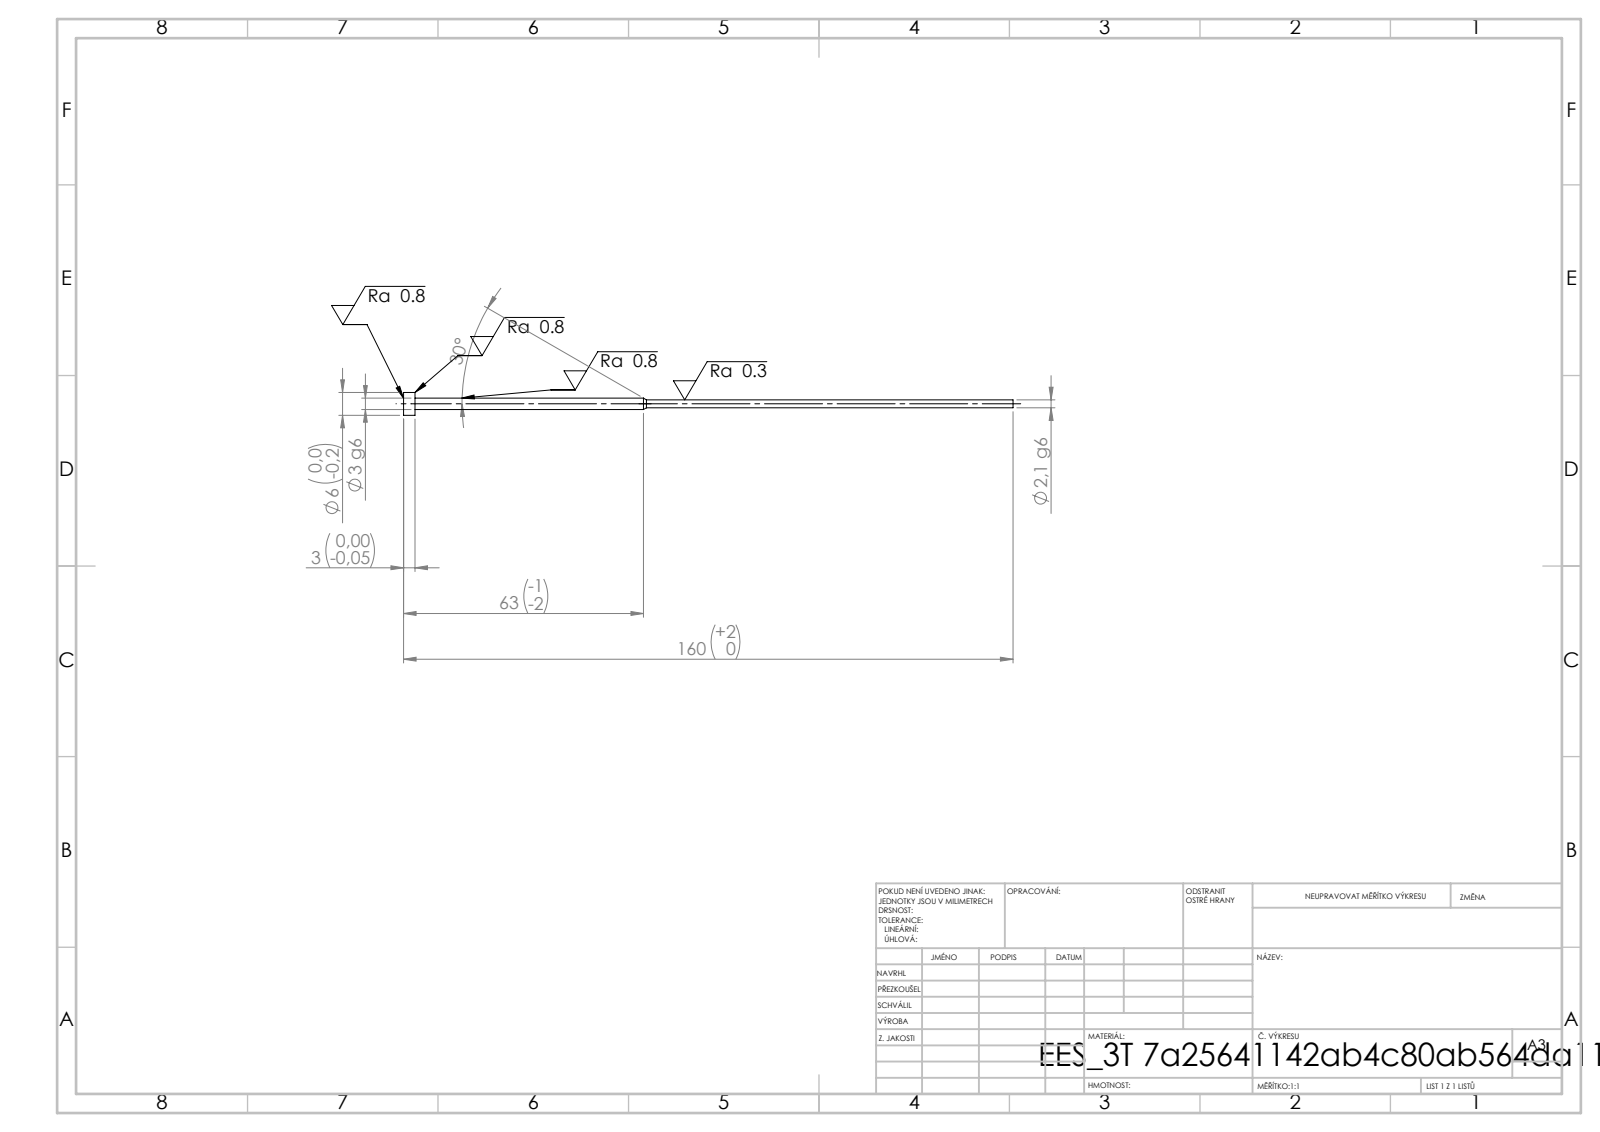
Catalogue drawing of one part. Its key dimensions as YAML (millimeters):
step_written_by: "SolidWorks 2019 (CONFIG_CONTROL_DESIGN)"
units: millimeters
bodies: {solids: 1, faces: 11, planar: 3, cylindrical: 6, other: 2}
overall_size: [160, 6, 6]
volume: 846
surface_area: 1317
round_bosses_or_shafts:
  - {diameter: 6, count: 1}
  - {diameter: 3, count: 1}
  - {diameter: 2.1, count: 1}
face_to_face_distances: [3, 157, 160]
